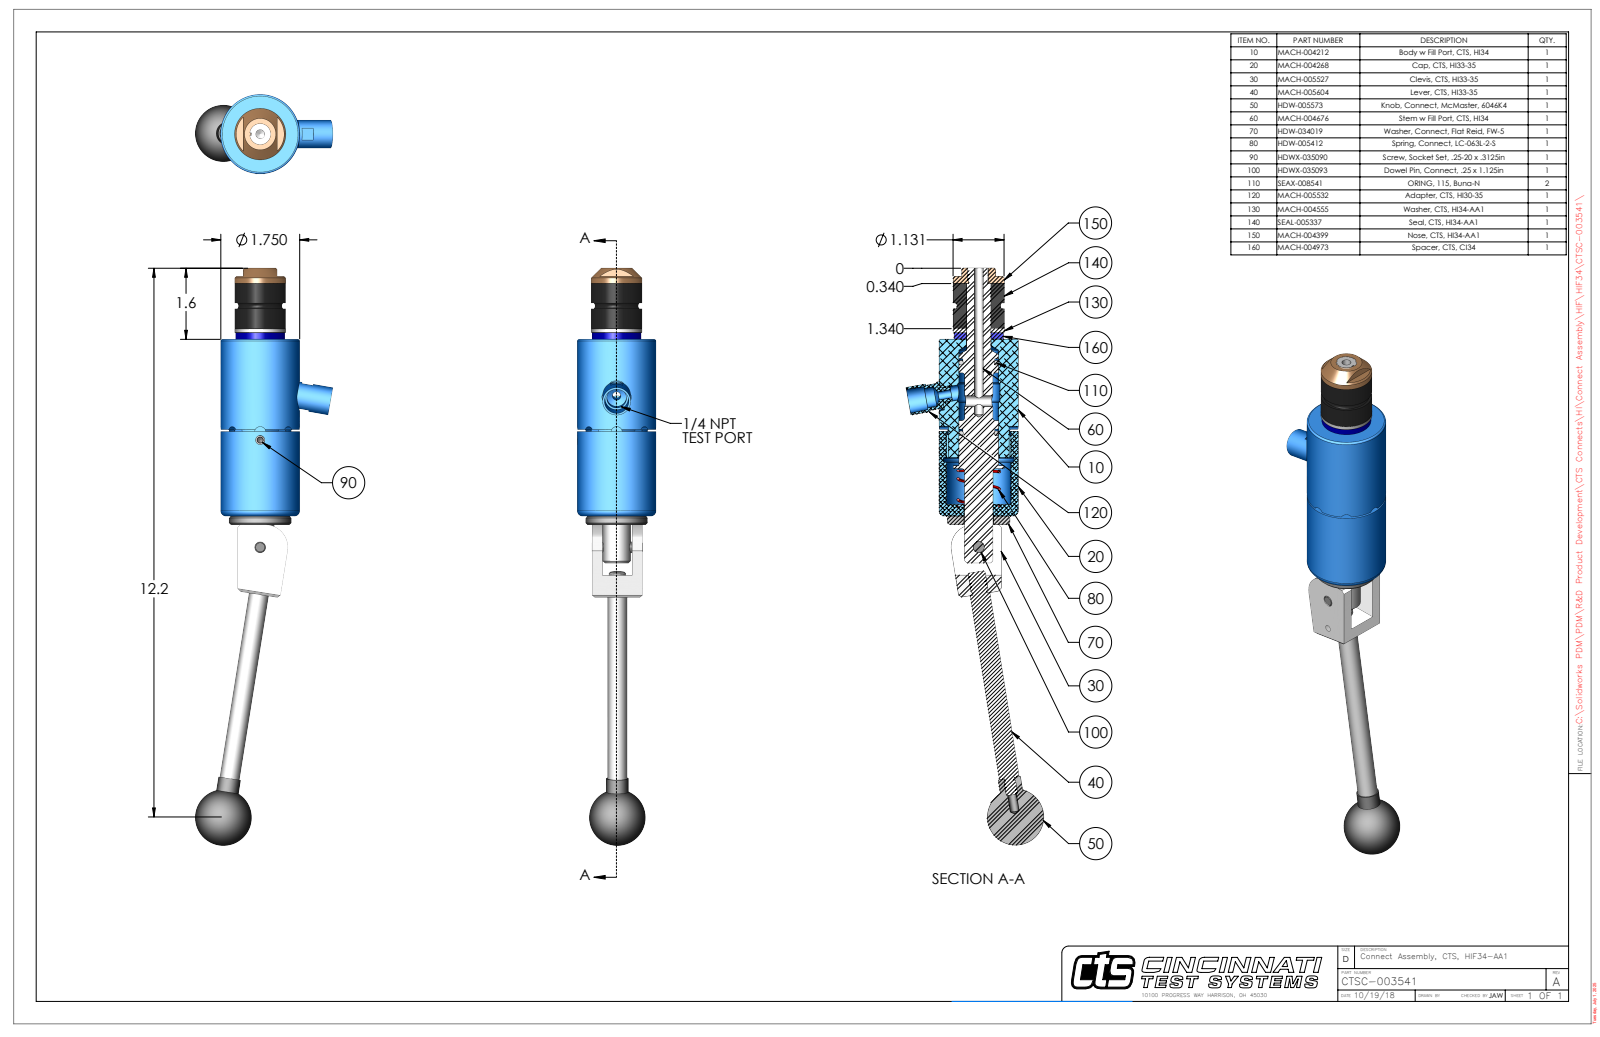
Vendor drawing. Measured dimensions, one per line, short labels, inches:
name: CTSC-003541
written by: SolidWorks 2023 (AUTOMOTIVE_DESIGN)
unit: in
bodies: 10 solids, 294 faces (106 planar, 122 cylindrical, 66 other)
size: 12.795 × 3.043 × 1.75
volume: 14.03 in³; area: 79.95 in²
holes: 2× ⌀0.201, 1× ⌀0.15, 1× ⌀0.187, 1× ⌀0.204, 1× ⌀0.249, 1× ⌀0.25, 1× ⌀0.251, 1× ⌀0.313, 1× ⌀0.422, 1× ⌀0.438, 1× ⌀0.53, 1× ⌀0.541
bosses: 2× ⌀0.5, 2× ⌀0.44, 2× ⌀0.25, 1× ⌀1.75, 1× ⌀1.38, 1× ⌀1.131, 1× ⌀1.09, 1× ⌀0.625
rounds: 4× R0.125, 2× R0.029, 1× R0.166, 1× R0.172, 1× R0.33, 1× R0.5, 1× R0.695, 1× R0.818
face distances: 3.921, 1.237, 5.158, 1, 0.237, 4.158, 1.12, 1.094, 0.094, 0.143
hole spacings: 0.74, 2.376, 3.116
